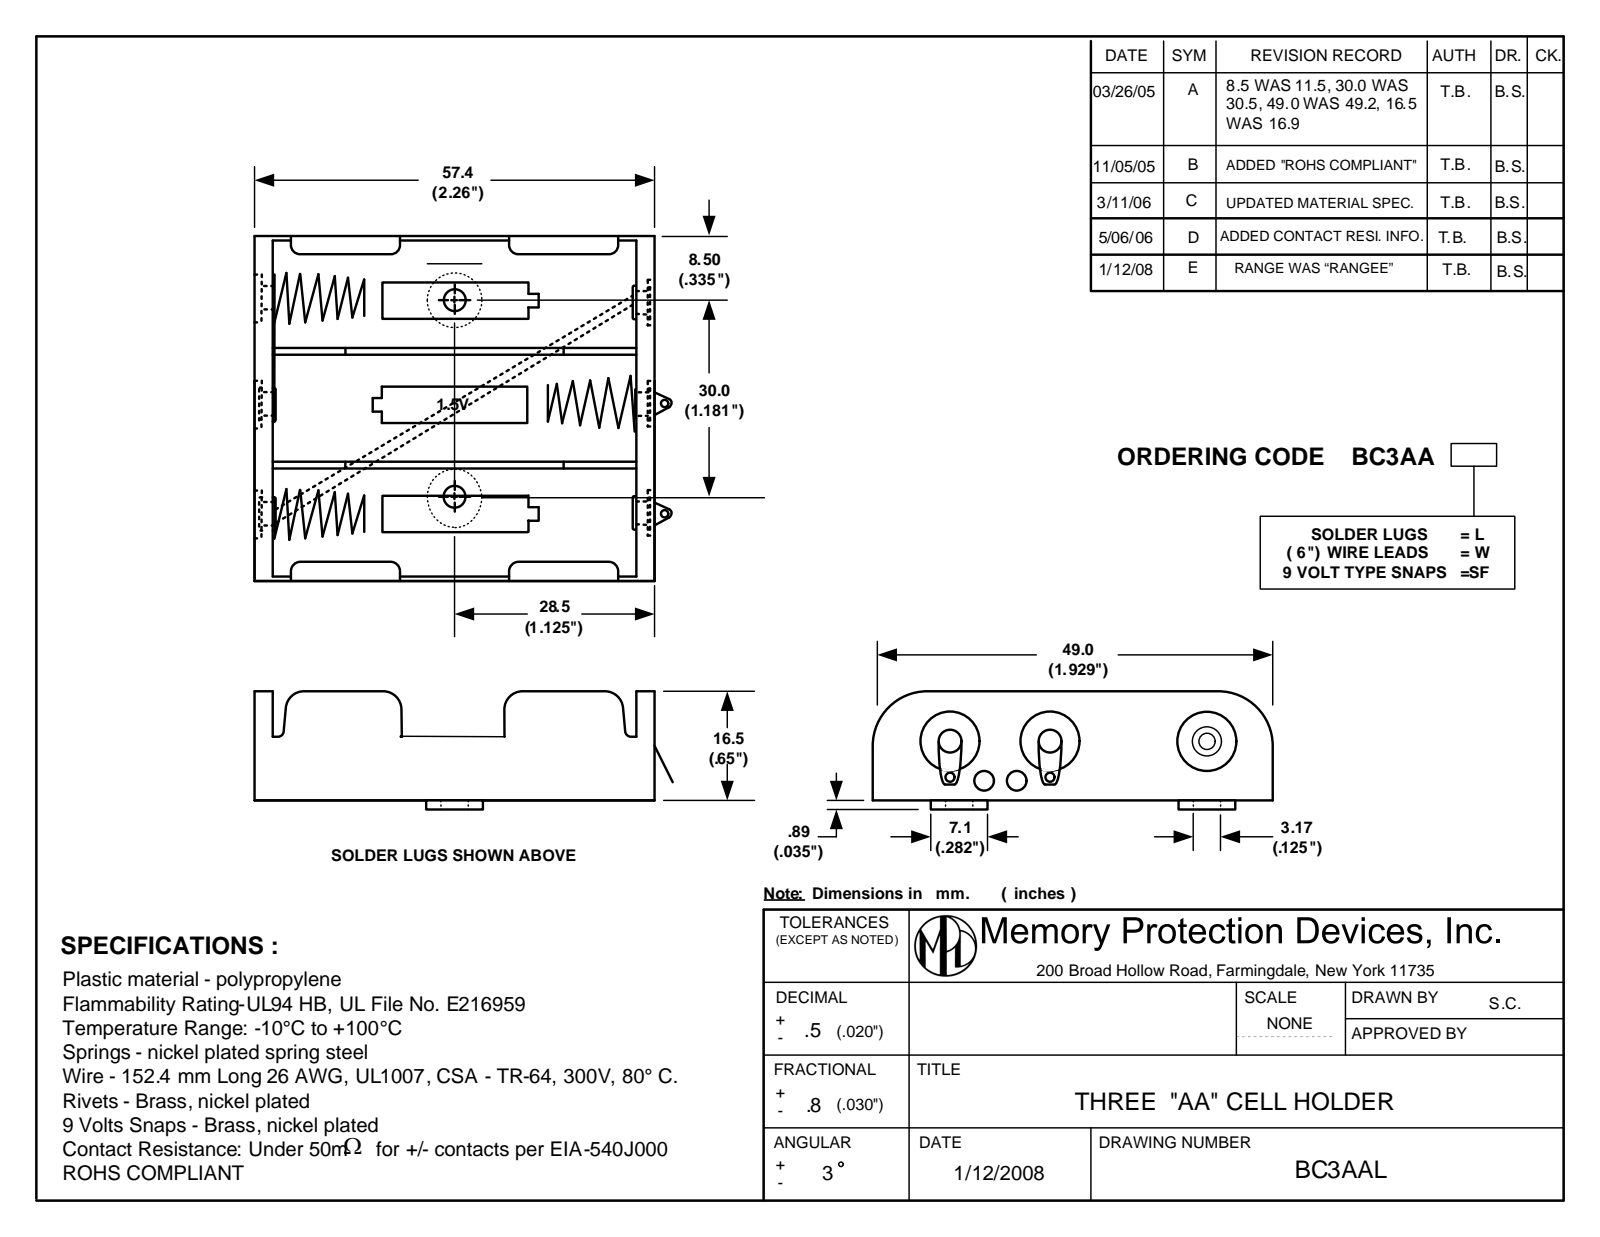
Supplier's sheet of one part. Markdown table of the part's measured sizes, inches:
| quantity | value |
| --- | --- |
| part name | BC3AAL |
| STEP written by | SolidWorks 2016 (AUTOMOTIVE_DESIGN) |
| units | inches |
| bodies | 8 solids, 484 faces (234 planar, 168 cylindrical, 82 other) |
| overall size | 2.367 × 1.929 × 0.65 |
| volume | 0.535 in³ |
| surface area | 23.58 in² |
| round holes (diameter × count) | 0.146 × 6, 0.079 × 5, 0.091 × 3, 0.118 × 3, 0.299 × 3, 0.031 × 2, 0.122 × 2, 0.197 × 2 |
| round bosses / shafts (diameter × count) | 0.185 × 6, 0.244 × 3, 0.138 × 3, 0.024 × 2, 0.028 × 1 |
| partial cylindrical surfaces (radius × count) | 0.098 × 8, 0.055 × 2, 0.118 × 2, 0.148 × 2, 0.157 × 2, 0.161 × 2, 0.354 × 1, 0.367 × 1 |
| main face-to-face distances | 0.043, 0.061, 2.217, 1.886, 0.643, 0.622, 1.265, 1.264, 0.621, 2.173 |
| hole center spacings | 0.643, 1.628, 0.643, 1.286, 1.496, 0.504, 0.742, 0.758 |
